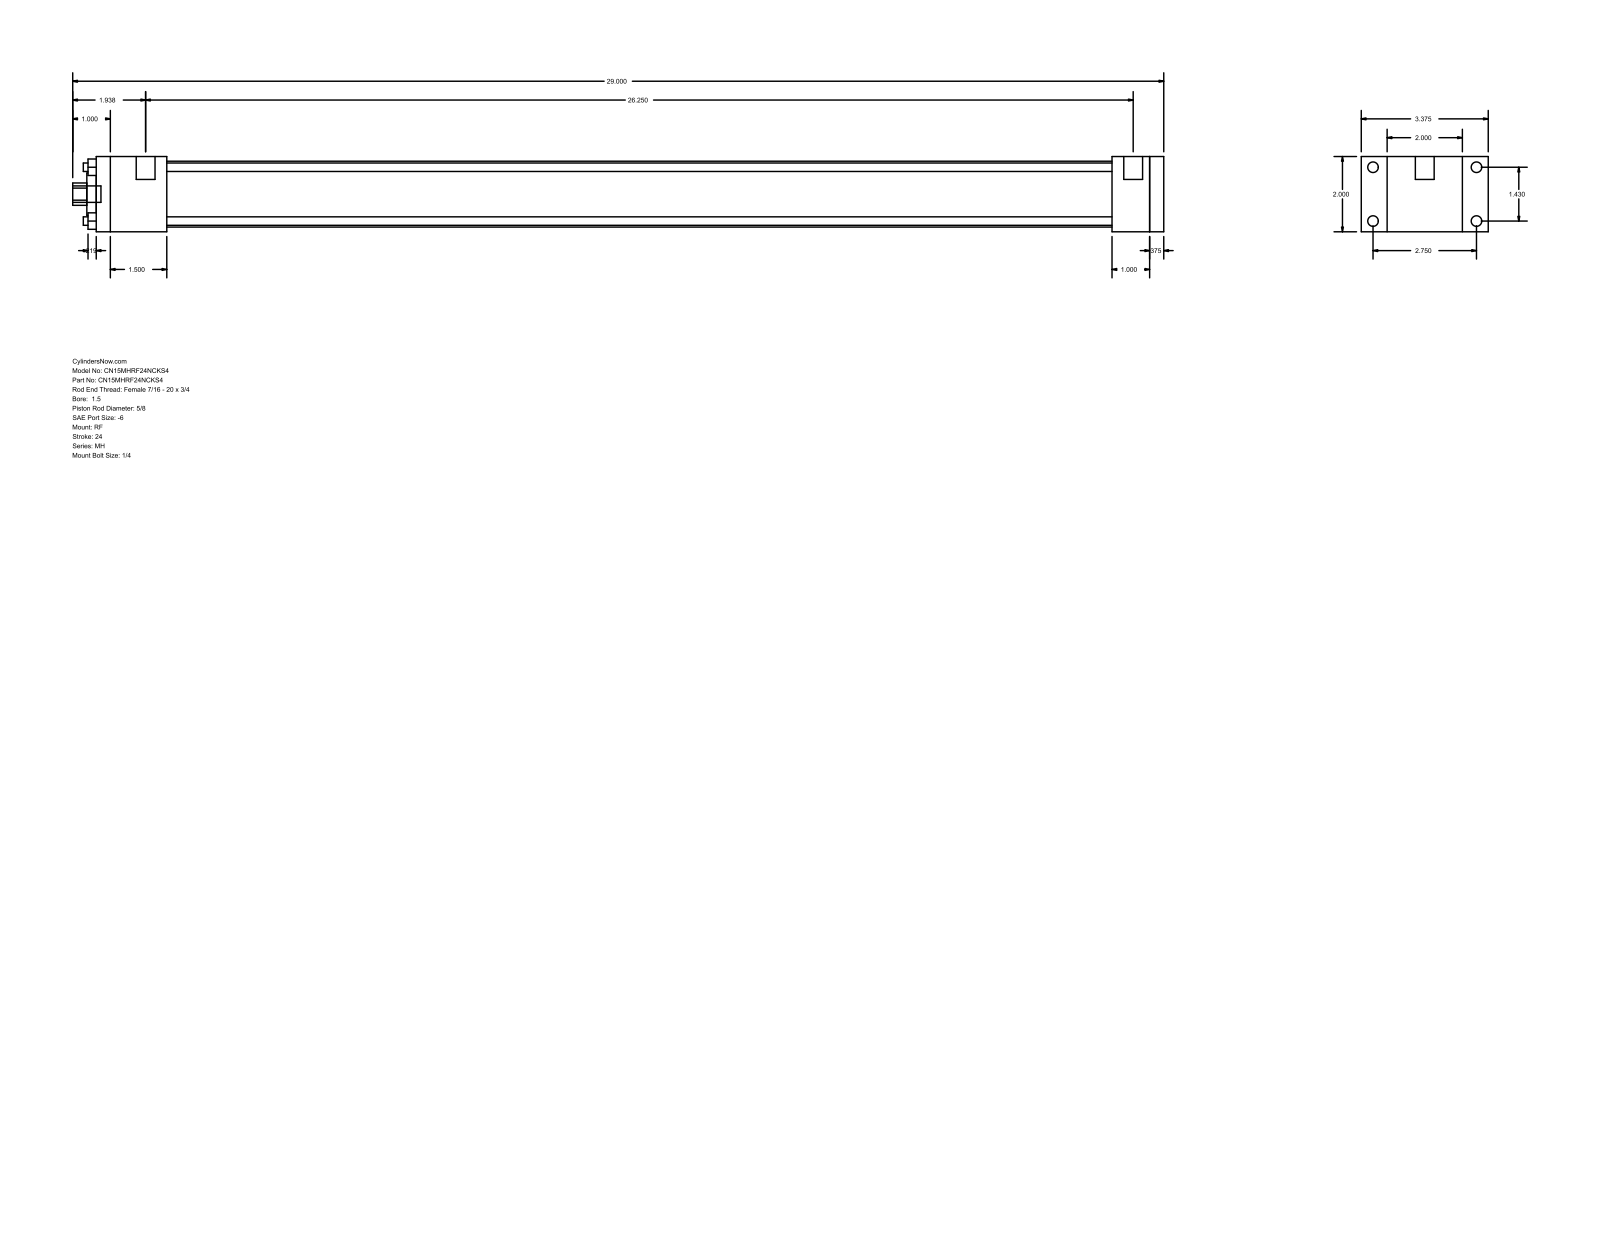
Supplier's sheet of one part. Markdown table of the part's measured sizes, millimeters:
| quantity | value |
| --- | --- |
| part name | MH_RF__0150_0.625 |
| STEP written by | GSSL Pune (CONFIG_CONTROL_DESIGN) |
| units | millimeters |
| bodies | 0 solids, 92 faces (64 planar, 28 cylindrical, 0 other) |
| overall size | 736.6 × 85.72 × 50.8 |
| round holes (diameter × count) | 5.71 × 4, 15.88 × 1, 28.57 × 1, 44.45 × 1 |
| round bosses / shafts (diameter × count) | 7.14 × 4, 5.56 × 4, 12.7 × 2, 11.11 × 1 |
| partial cylindrical surfaces (radius × count) | 7.54 × 1 |
| main face-to-face distances | 50.8, 9.52, 711.2, 720.72, 17.46, 68.26, 685.79, 25.41, 34.93, 47.62 |
| hole center spacings | 25.68, 36.32, 51.36 |
